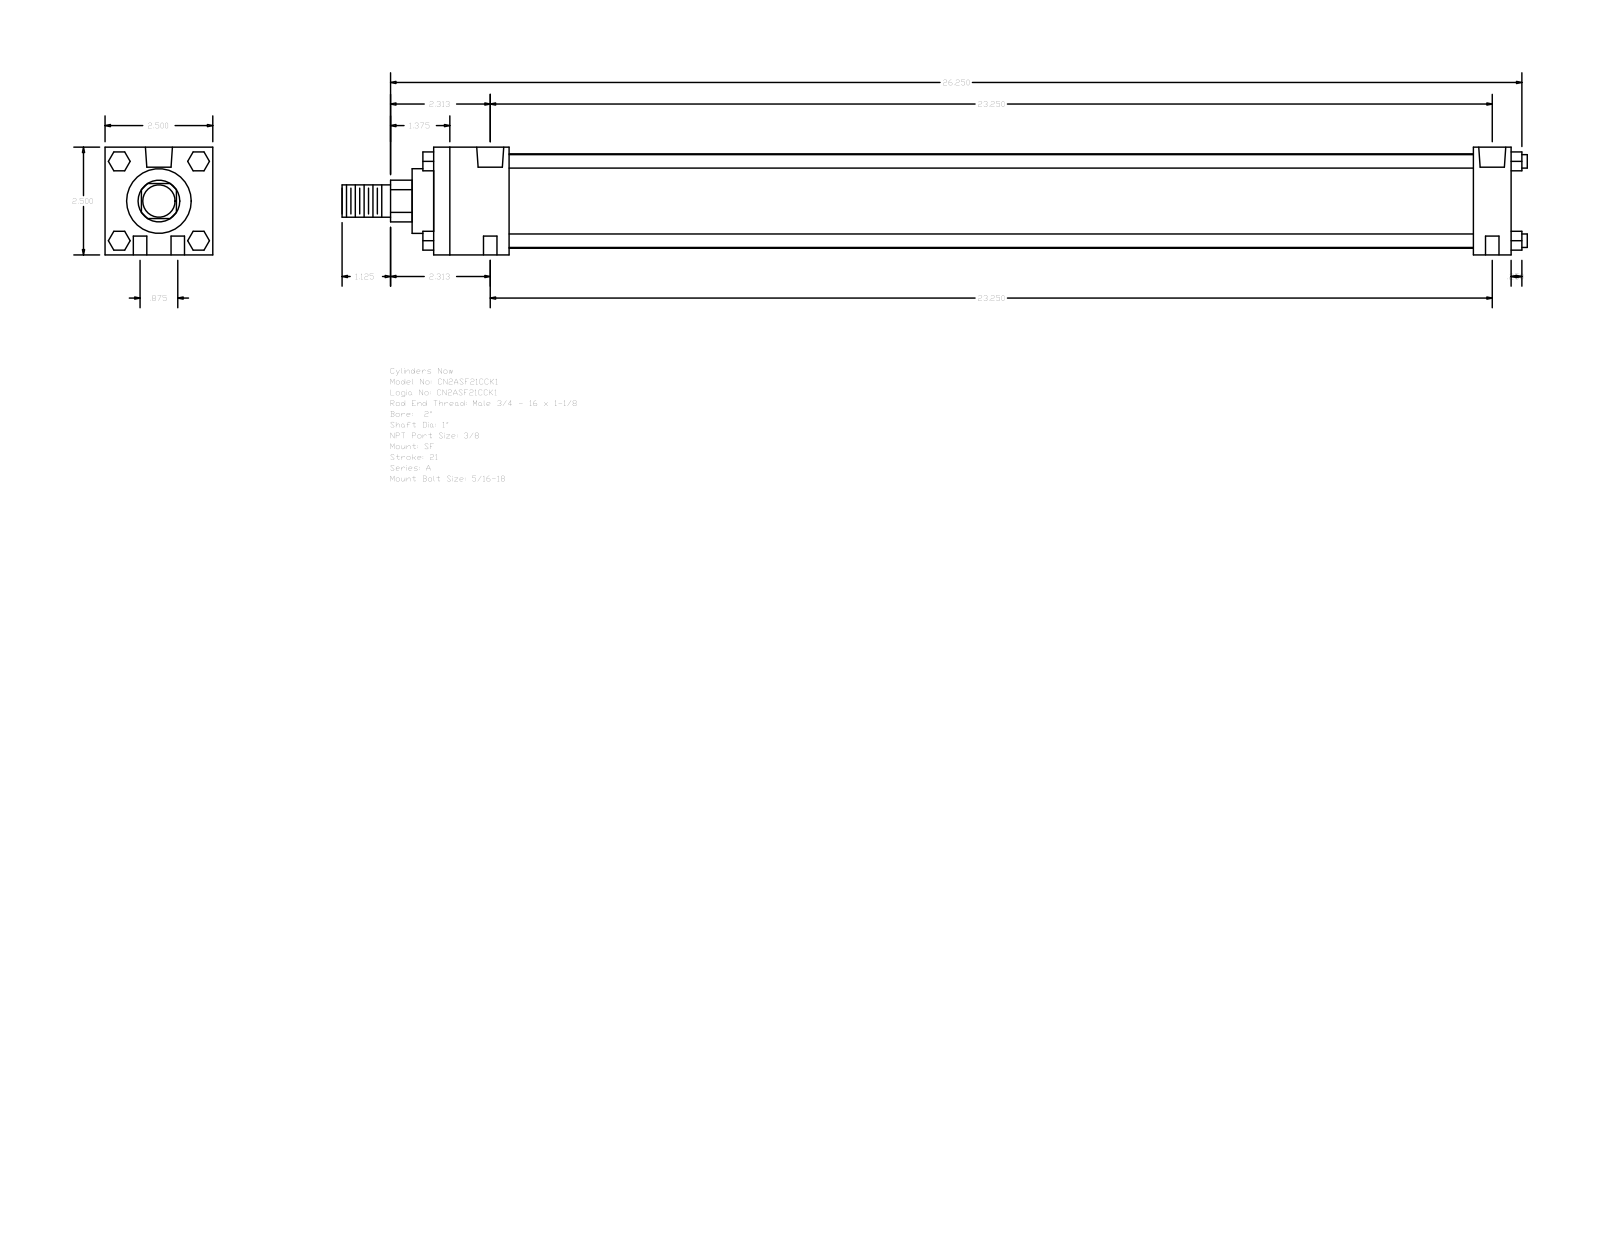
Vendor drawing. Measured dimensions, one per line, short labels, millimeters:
name: A_SF__0200_1
written by: GSSL Pune (CONFIG_CONTROL_DESIGN)
unit: mm
bodies: 0 solids, 124 faces (94 planar, 30 cylindrical, 0 other)
size: 698.5 × 63.5 × 63.5
holes: 4× ⌀7.94, 2× ⌀5.56, 2× ⌀15.93
bosses: 4× ⌀7.94, 1× ⌀55.63, 1× ⌀38.1, 1× ⌀25.4, 1× ⌀19.05
rounds: 1× R12.29
face distances: 63.5, 635, 612.77, 22.23, 44.45, 568.32, 590.55, 12.7, 647.7, 6.35
hole spacings: 11.11, 590.65, 590.55, 22.22, 590.97, 584.98
